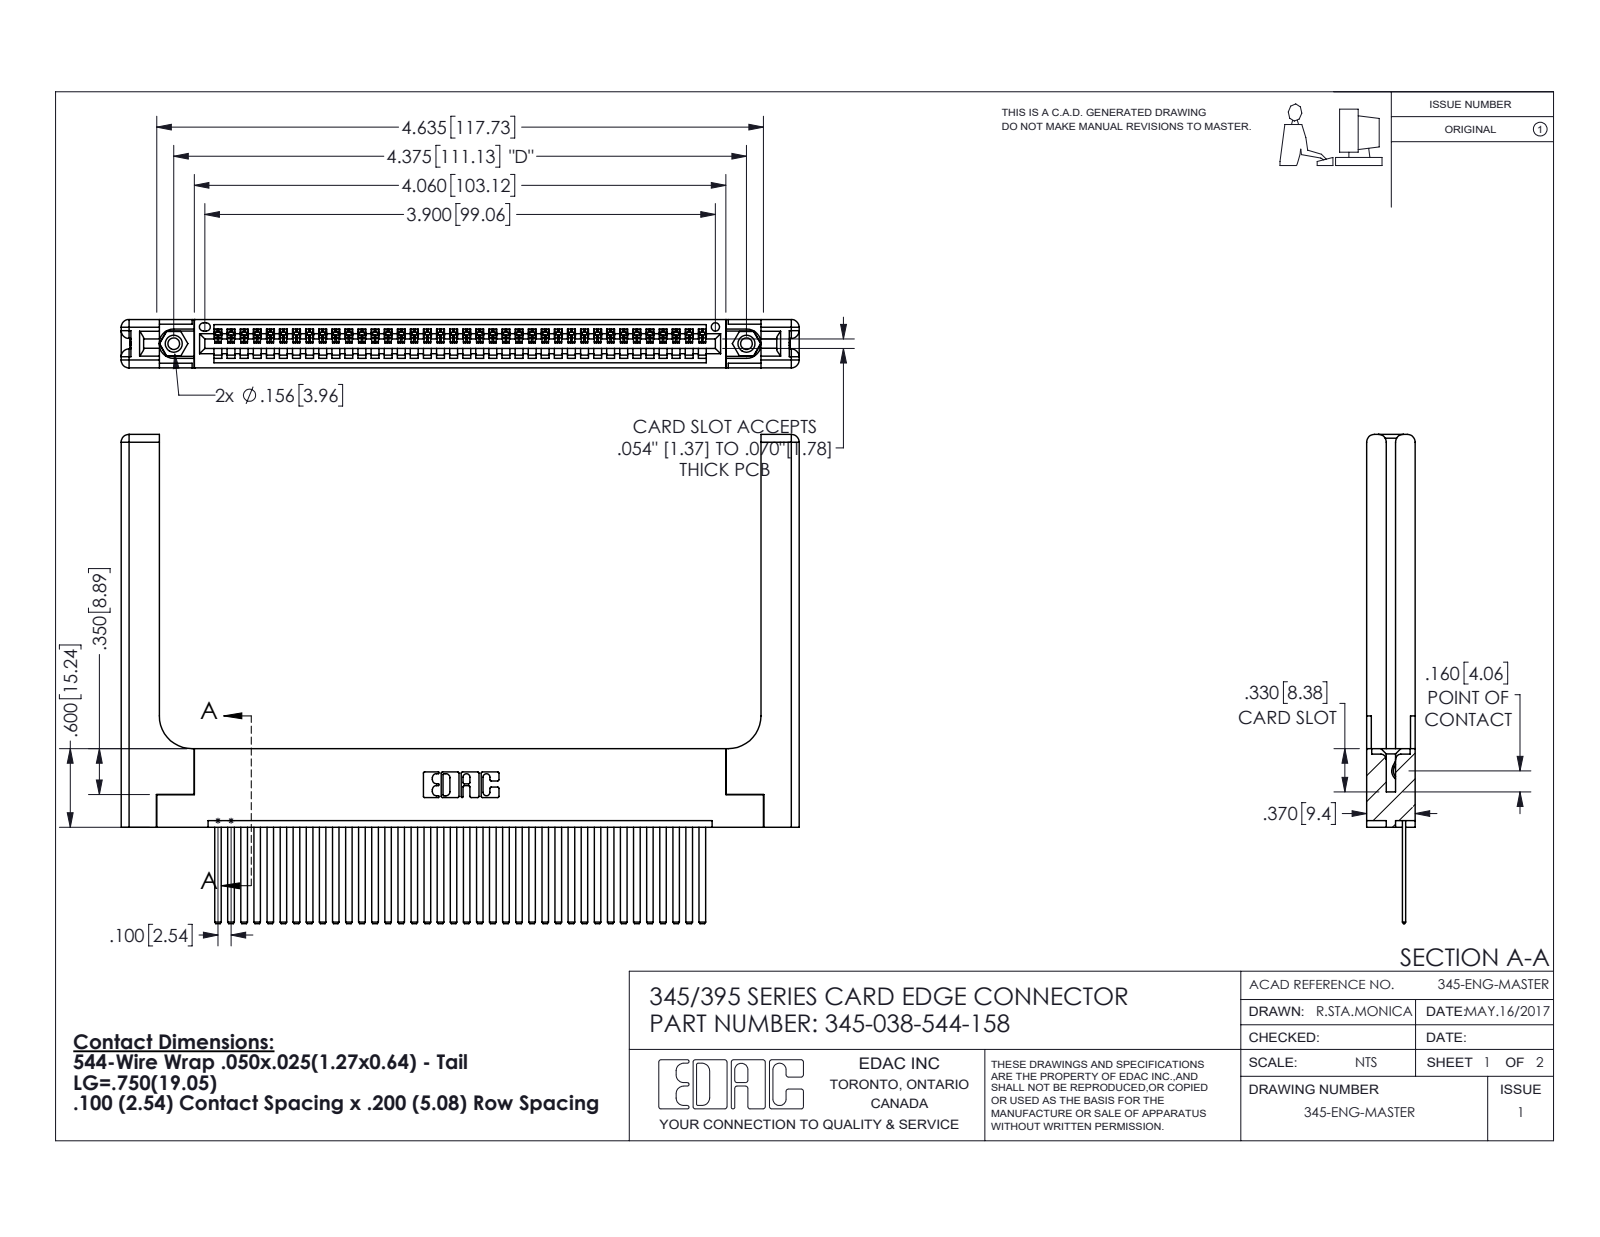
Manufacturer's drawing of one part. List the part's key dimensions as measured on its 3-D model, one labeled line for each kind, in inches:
Part name (STEP PRODUCT): 345-038-544-158; 345-250-001_345-250-001-102; 345-220-058_345-220-058; 345-292-001_345-293-144 (+1 more)
STEP written by: SolidWorks 2016 (CONFIG_CONTROL_DESIGN)
Units: inches
Bodies: 43 solids, 2358 faces (1596 planar, 702 cylindrical, 60 other)
Overall size (bounding box): 5.179 × 3.737 × 0.37
Volume: 1.306 in³ · Surface area: 36.76 in²
Round holes (diameter × count): ⌀0.089 ×2, ⌀0.125 ×2, ⌀0.156 ×2, ⌀0.064 ×1
Round bosses / shafts (diameter × count): ⌀0.155 ×2
Partial cylindrical surfaces — rounded edges, fillets, slot ends (radius × count): R0.006 ×76, R0.01 ×22, R0.06 ×16, R0.007 ×6, R0.031 ×6, R0.026 ×3, R0.03 ×2, R0.031 ×2
Main face-to-face distances: 0.072, 0.298, 0.37, 0.098, 0.272, 0.025, 0.2, 0.148, 0.15, 0.225
Hole centre spacings: 0.27, 4.139, 4.375
